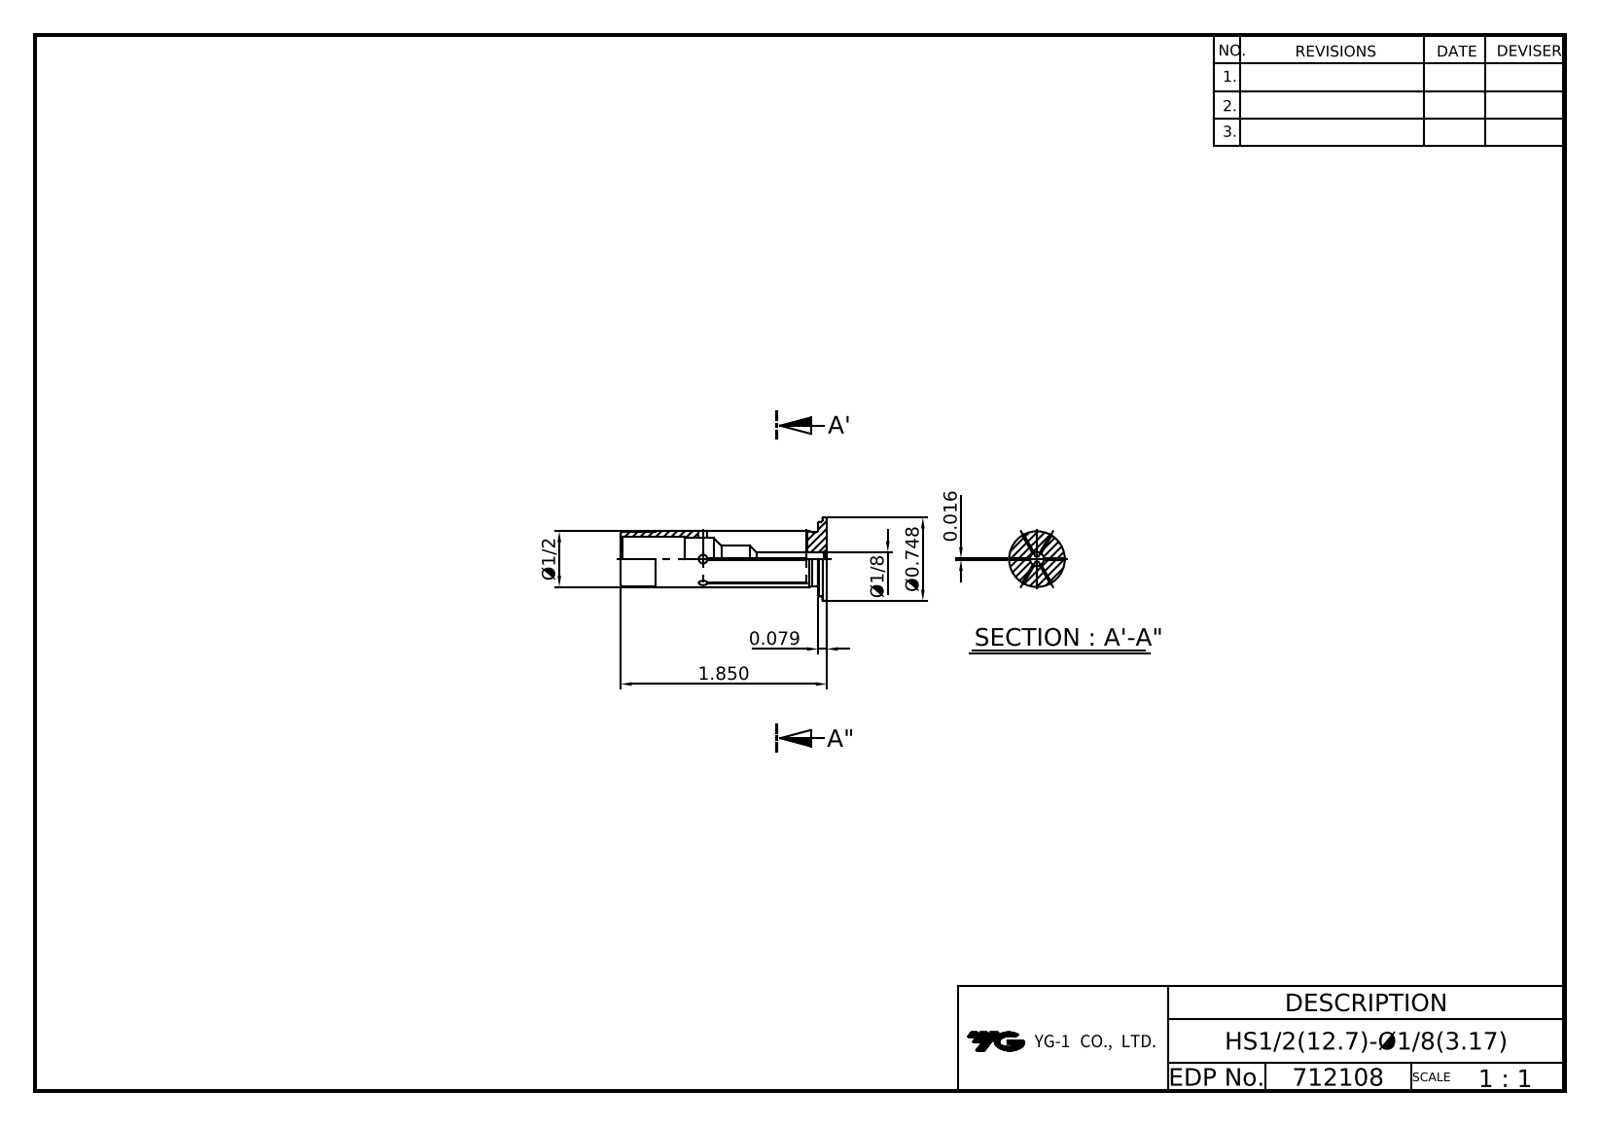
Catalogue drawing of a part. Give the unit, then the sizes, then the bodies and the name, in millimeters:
Units: millimetres
Overall size (bounding box): 47 × 19 × 19
Round holes (diameter × count): ⌀3.17 ×1, ⌀6 ×1, ⌀9.6 ×1, ⌀10 ×1
Round bosses / shafts (diameter × count): ⌀19 ×1, ⌀17 ×1, ⌀12.7 ×1
Main face-to-face distances: 1, 2, 45, 46, 47
Volume: 4 164 mm³ · Surface area: 3 424 mm²
Bodies: 1 solid, 14 faces (4 planar, 7 cylindrical, 3 other)
Part name (STEP PRODUCT): LO-HS12.7-3.175
STEP written by: Autodesk Inventor 2022 (AUTOMOTIVE_DESIGN)
